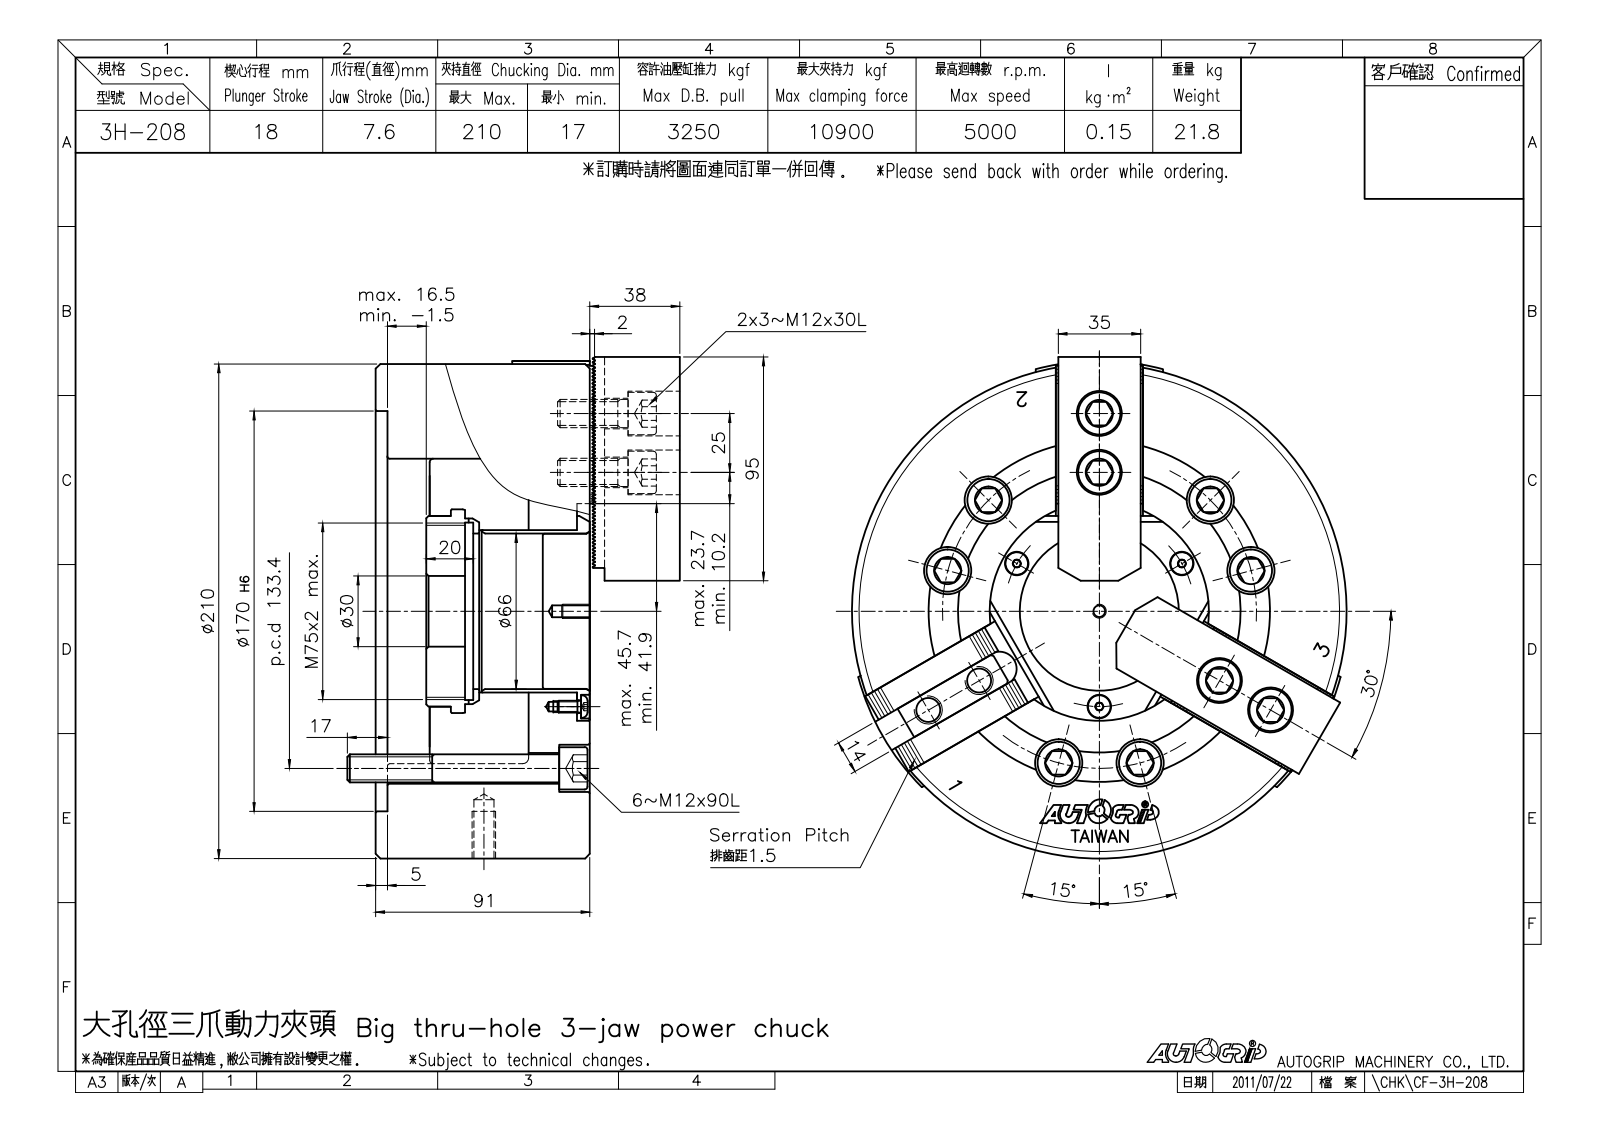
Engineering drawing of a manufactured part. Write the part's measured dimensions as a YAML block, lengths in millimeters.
part_name: "M12x90; SJ-08; CF-3H-208-02010; CF-3H-208-06000 (+5 more)"
step_written_by: "SolidWorks 2016 (CONFIG_CONTROL_DESIGN)"
units: millimeters
bodies: {solids: 23, faces: 2018, planar: 1448, cylindrical: 485, other: 85}
overall_size: [212.92, 210, 140]
volume: 2966000
surface_area: 371599
round_holes:
  - {diameter: 13, count: 12}
  - {diameter: 19, count: 6}
  - {diameter: 20, count: 6}
  - {diameter: 5, count: 4}
  - {diameter: 4.2, count: 3}
  - {diameter: 5.5, count: 3}
  - {diameter: 10, count: 3}
  - {diameter: 53, count: 1}
  - {diameter: 58, count: 1}
  - {diameter: 60.3, count: 1}
  - {diameter: 66, count: 1}
  - {diameter: 69, count: 1}
round_bosses_or_shafts:
  - {diameter: 18, count: 12}
  - {diameter: 12, count: 12}
  - {diameter: 9.5, count: 3}
  - {diameter: 5, count: 3}
  - {diameter: 210, count: 1}
  - {diameter: 78.8, count: 1}
  - {diameter: 65.8, count: 1}
partial_cylinders:
  - {radius: 0.1, count: 192}
face_to_face_distances: [62.5, 42.5, 91, 5, 35, 0.5, 18, 20, 65, 26]
hole_center_spacings: [99.54, 101.5, 112.53, 115.53, 124.55, 130.95, 149.35, 20.24]
